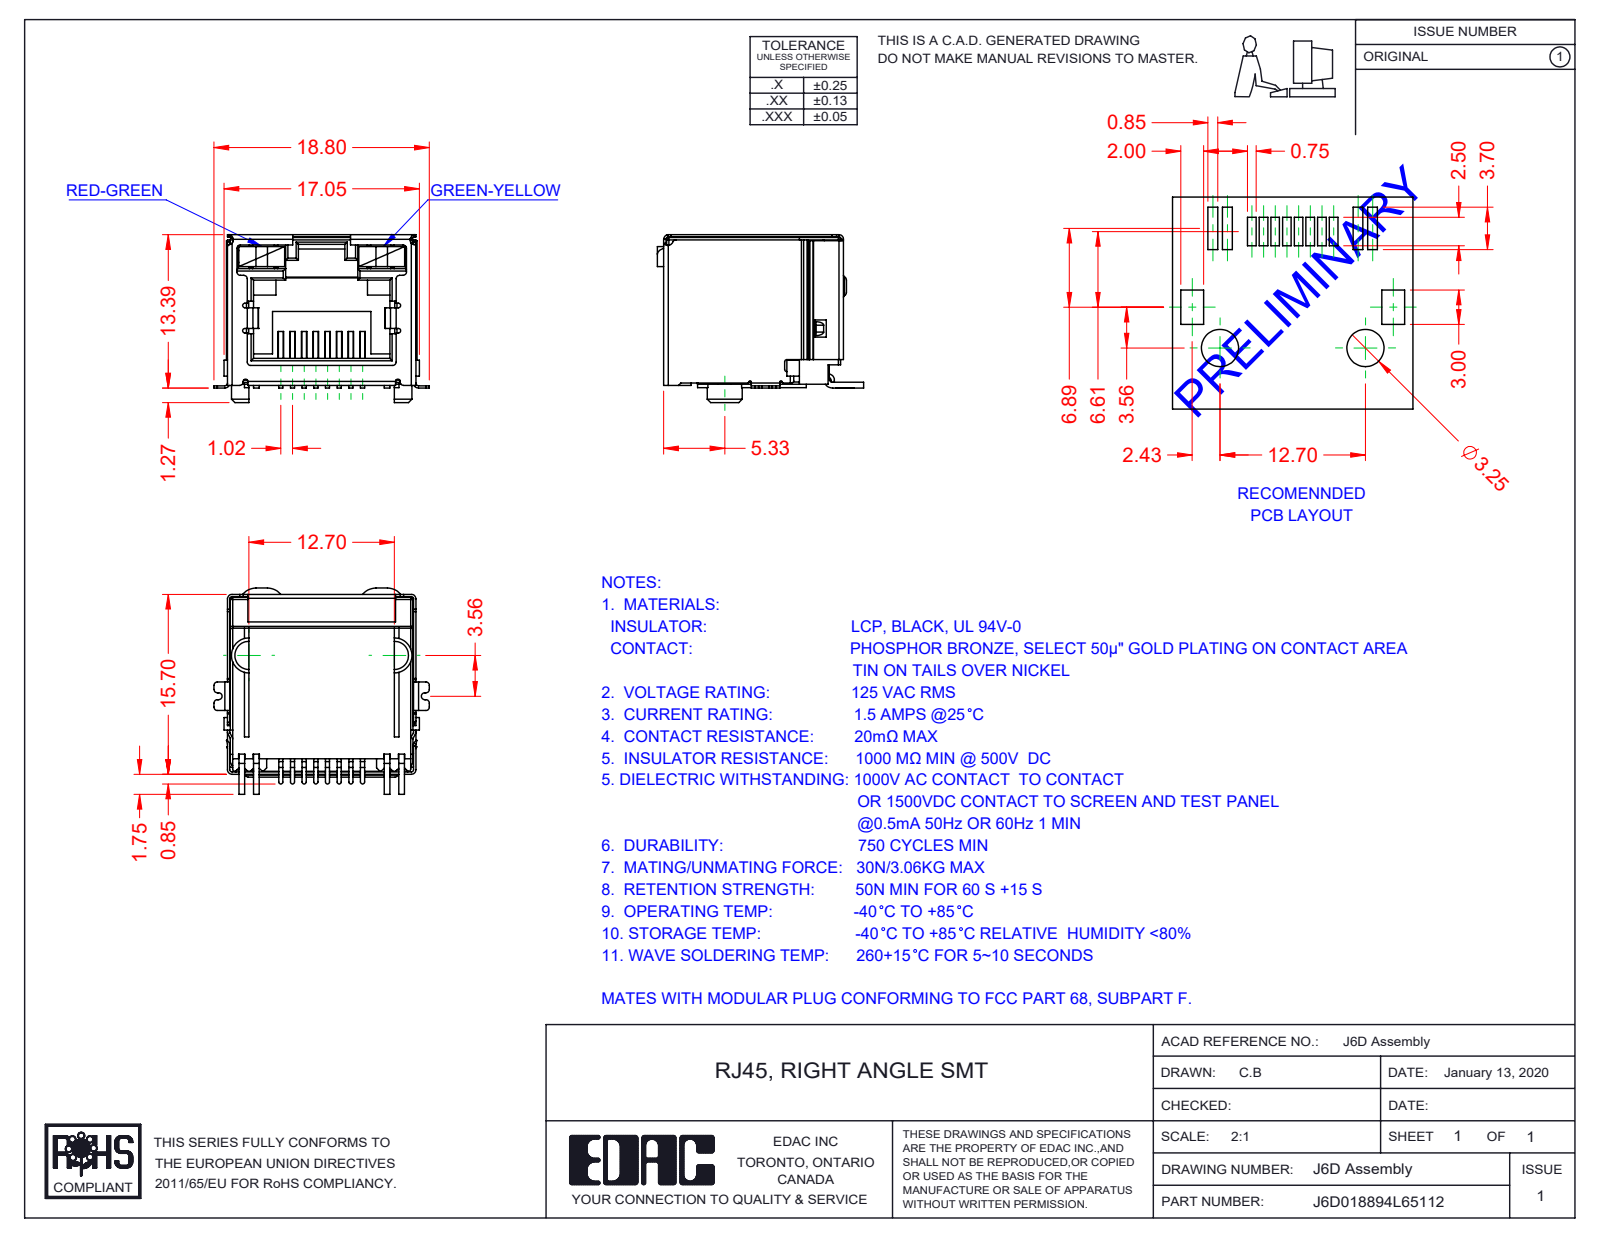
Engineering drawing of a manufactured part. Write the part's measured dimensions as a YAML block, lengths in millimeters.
part_name: "6D Contacts; 6D LED RH_5-Green-Yellow; 6D Insulator; 6D Shield_LED - No EMI (+2 more)"
step_written_by: "SolidWorks 2016 (CONFIG_CONTROL_DESIGN)"
units: millimeters
bodies: {solids: 12, faces: 899, planar: 646, cylindrical: 220, other: 33}
overall_size: [18.8, 18, 14.65]
volume: 1804
surface_area: 4898
partial_cylinders:
  - {radius: 0.3, count: 39}
  - {radius: 0.2, count: 37}
  - {radius: 0.4, count: 16}
  - {radius: 0.1, count: 12}
  - {radius: 0.15, count: 8}
  - {radius: 0.18, count: 8}
  - {radius: 0.5, count: 6}
  - {radius: 1.5, count: 5}
face_to_face_distances: [16, 16.25, 16.2, 2.25, 1, 15.95, 16.05, 12.8, 0.45, 16.45]
